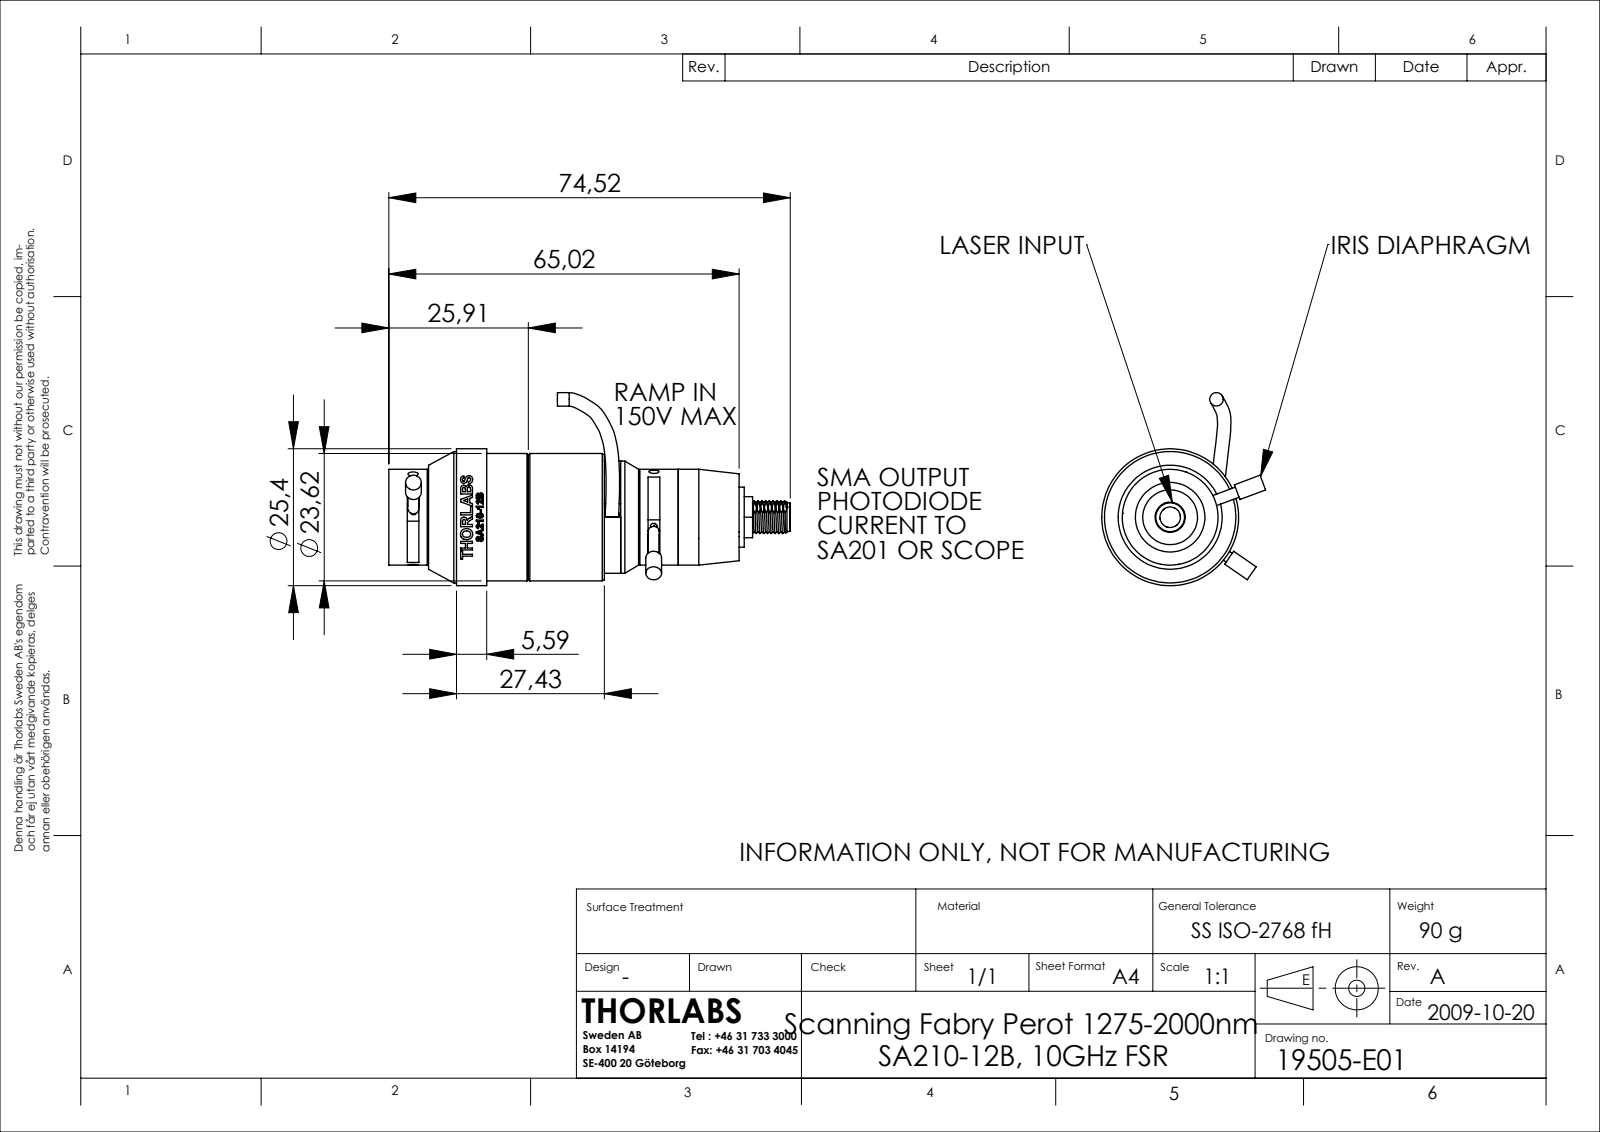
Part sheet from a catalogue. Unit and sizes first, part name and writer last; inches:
Units: inches
Overall size (bounding box): 2.934 × 1.41 × 1.197
Round holes (diameter × count): ⌀0.058 ×10, ⌀0.075 ×6, ⌀0.039 ×1, ⌀0.106 ×1, ⌀0.15 ×1, ⌀0.181 ×1, ⌀0.22 ×1, ⌀0.24 ×1, ⌀0.25 ×1, ⌀0.325 ×1, ⌀0.385 ×1, ⌀0.395 ×1
Round bosses / shafts (diameter × count): ⌀0.115 ×2, ⌀0.078 ×2, ⌀1 ×1, ⌀0.96 ×1, ⌀0.93 ×1, ⌀0.92 ×1, ⌀0.906 ×1, ⌀0.82 ×1
Partial cylindrical surfaces — rounded edges, fillets, slot ends (radius × count): R0.014 ×1, R0.02 ×1, R0.055 ×1, R0.063 ×1, R0.075 ×1, R0.11 ×1, R0.125 ×1, R0.282 ×1
Main face-to-face distances: 0.29, 0.1, 1.725, 0.15, 1.825, 0.08, 0.13, 1.285, 1.575, 0.44
Hole centre spacings: 0.148, 0.257, 0.297, 0.137, 0.263, 0.013, 0.16, 0.25
Volume: 0.465 in³ · Surface area: 22.59 in²
Bodies: 9 solids, 416 faces (160 planar, 181 cylindrical, 75 other)
Part name (STEP PRODUCT): 8655-013; 6902-E0W; kabel; SW3dPS-SMA Nut (+7 more)
STEP written by: SolidWorks 2009 (CONFIG_CONTROL_DESIGN)
